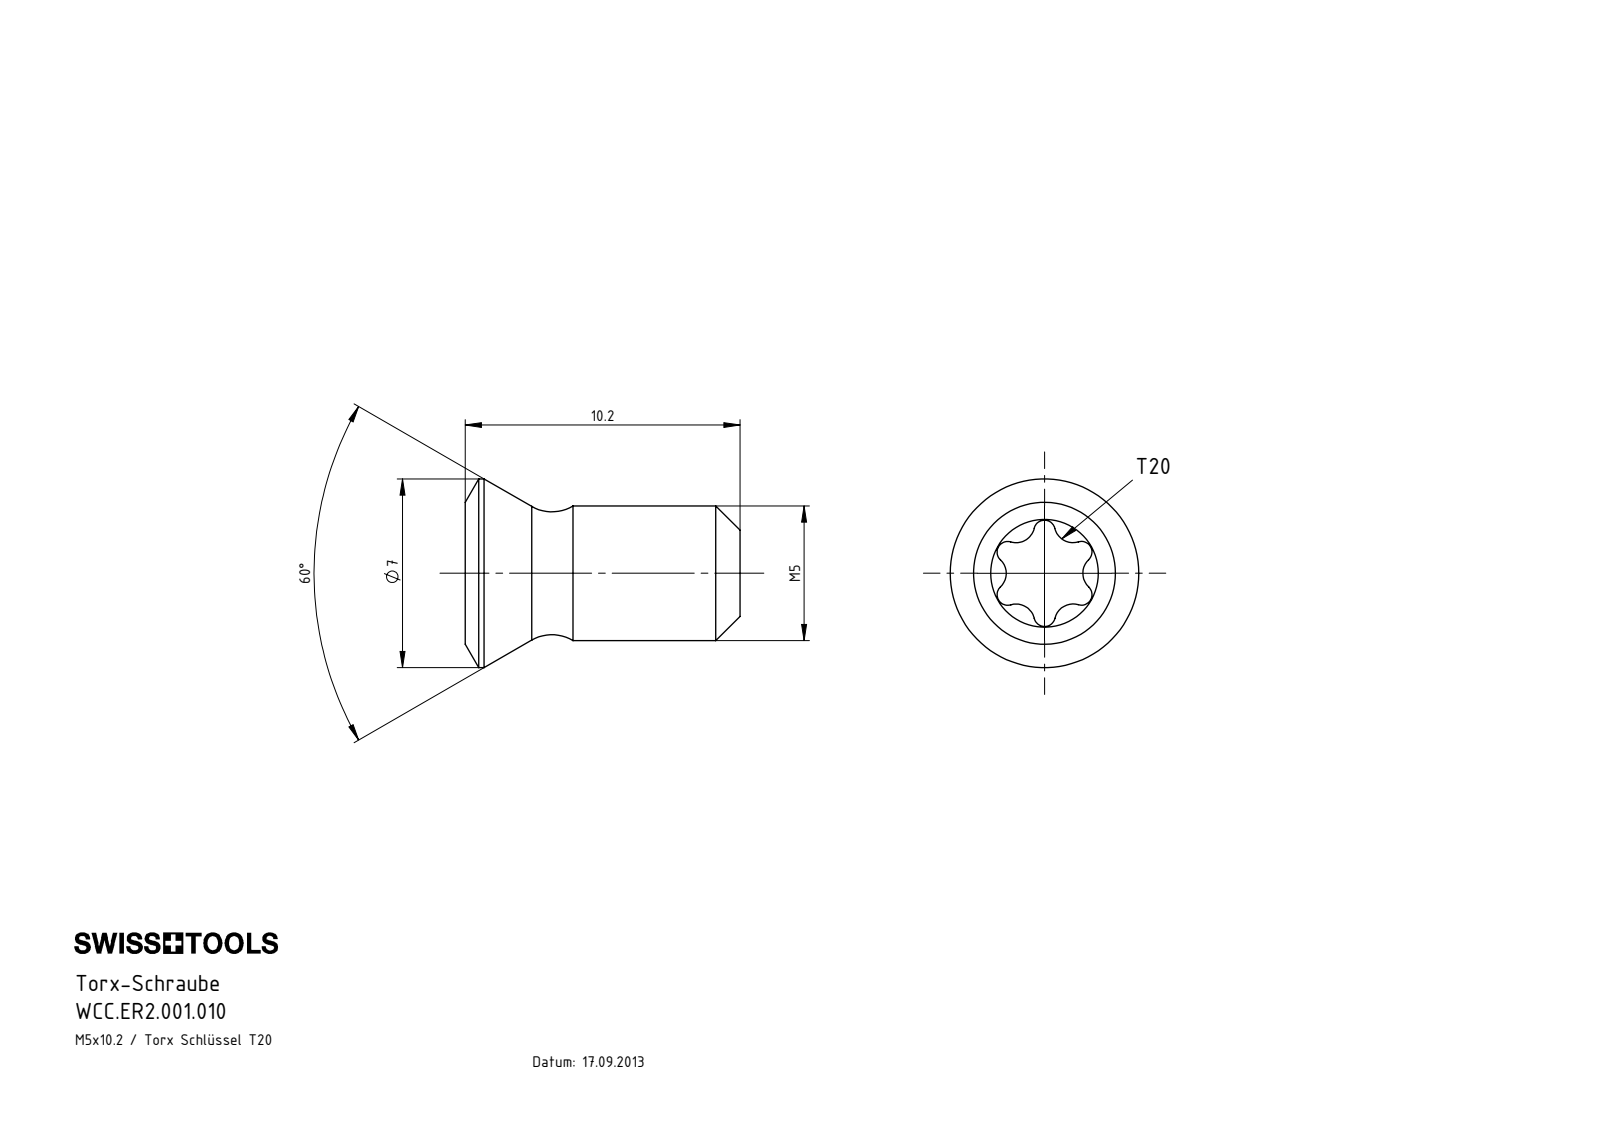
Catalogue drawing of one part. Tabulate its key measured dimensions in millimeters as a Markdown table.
| quantity | value |
| --- | --- |
| part name | WCC.ER2.001.010 |
| STEP written by | SolidWorks 2017 (AUTOMOTIVE_DESIGN) |
| units | millimeters |
| bodies | 1 solid, 34 faces (3 planar, 19 cylindrical, 12 other) |
| overall size | 10.2 × 7 × 7 |
| volume | 200 mm³ |
| surface area | 237 mm² |
| round bosses / shafts (diameter × count) | 7 × 1, 5 × 1 |
| partial cylindrical surfaces (radius × count) | 0.39 × 6, 0.69 × 3, 0.69 × 3 |
| main face-to-face distances | 1.7, 10.2, 8.5 |
